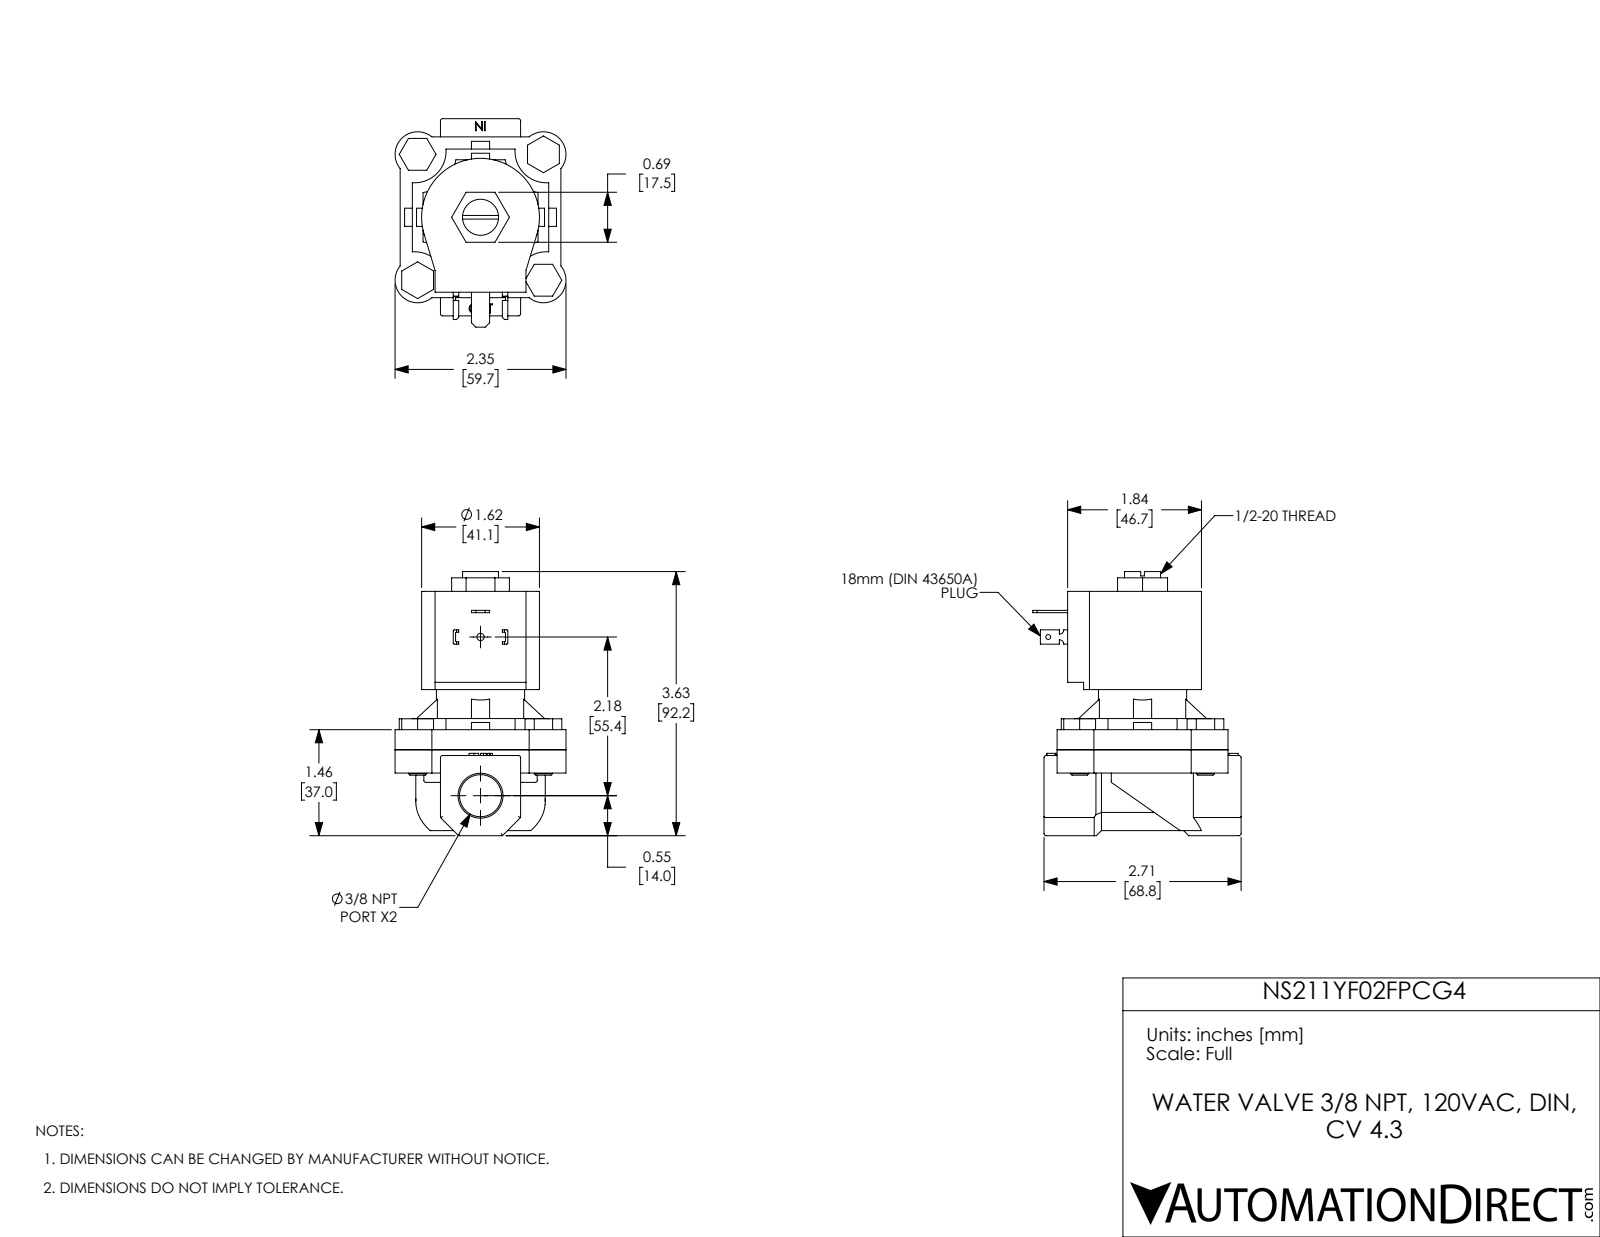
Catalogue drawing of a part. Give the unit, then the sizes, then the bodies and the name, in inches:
Units: inches
Overall size (bounding box): 3.63 × 2.865 × 2.35
Round holes (diameter × count): ⌀0.25 ×4, ⌀0.067 ×1, ⌀0.1 ×1, ⌀0.496 ×1, ⌀0.512 ×1, ⌀0.578 ×1, ⌀1.155 ×1
Round bosses / shafts (diameter × count): ⌀0.248 ×4, ⌀1.213 ×1
Partial cylindrical surfaces — rounded edges, fillets, slot ends (radius × count): R0.03 ×15, R0.015 ×8, R0.31 ×4, R0.432 ×4, R0.579 ×4, R0.06 ×2, R0.81 ×1, R0.89 ×1
Main face-to-face distances: 0.276, 2.177, 1.901, 0.32, 0.596, 2.497, 0.554, 1.656, 0.25, 1.147
Hole centre spacings: 1.223, 1.73, 2.446, 2.181
Volume: 9.675 in³ · Surface area: 64.2 in²
Bodies: 11 solids, 383 faces (237 planar, 113 cylindrical, 33 other)
Part name (STEP PRODUCT): NS211YF02FPCG4
STEP written by: SolidWorks 2017 (AUTOMOTIVE_DESIGN)
